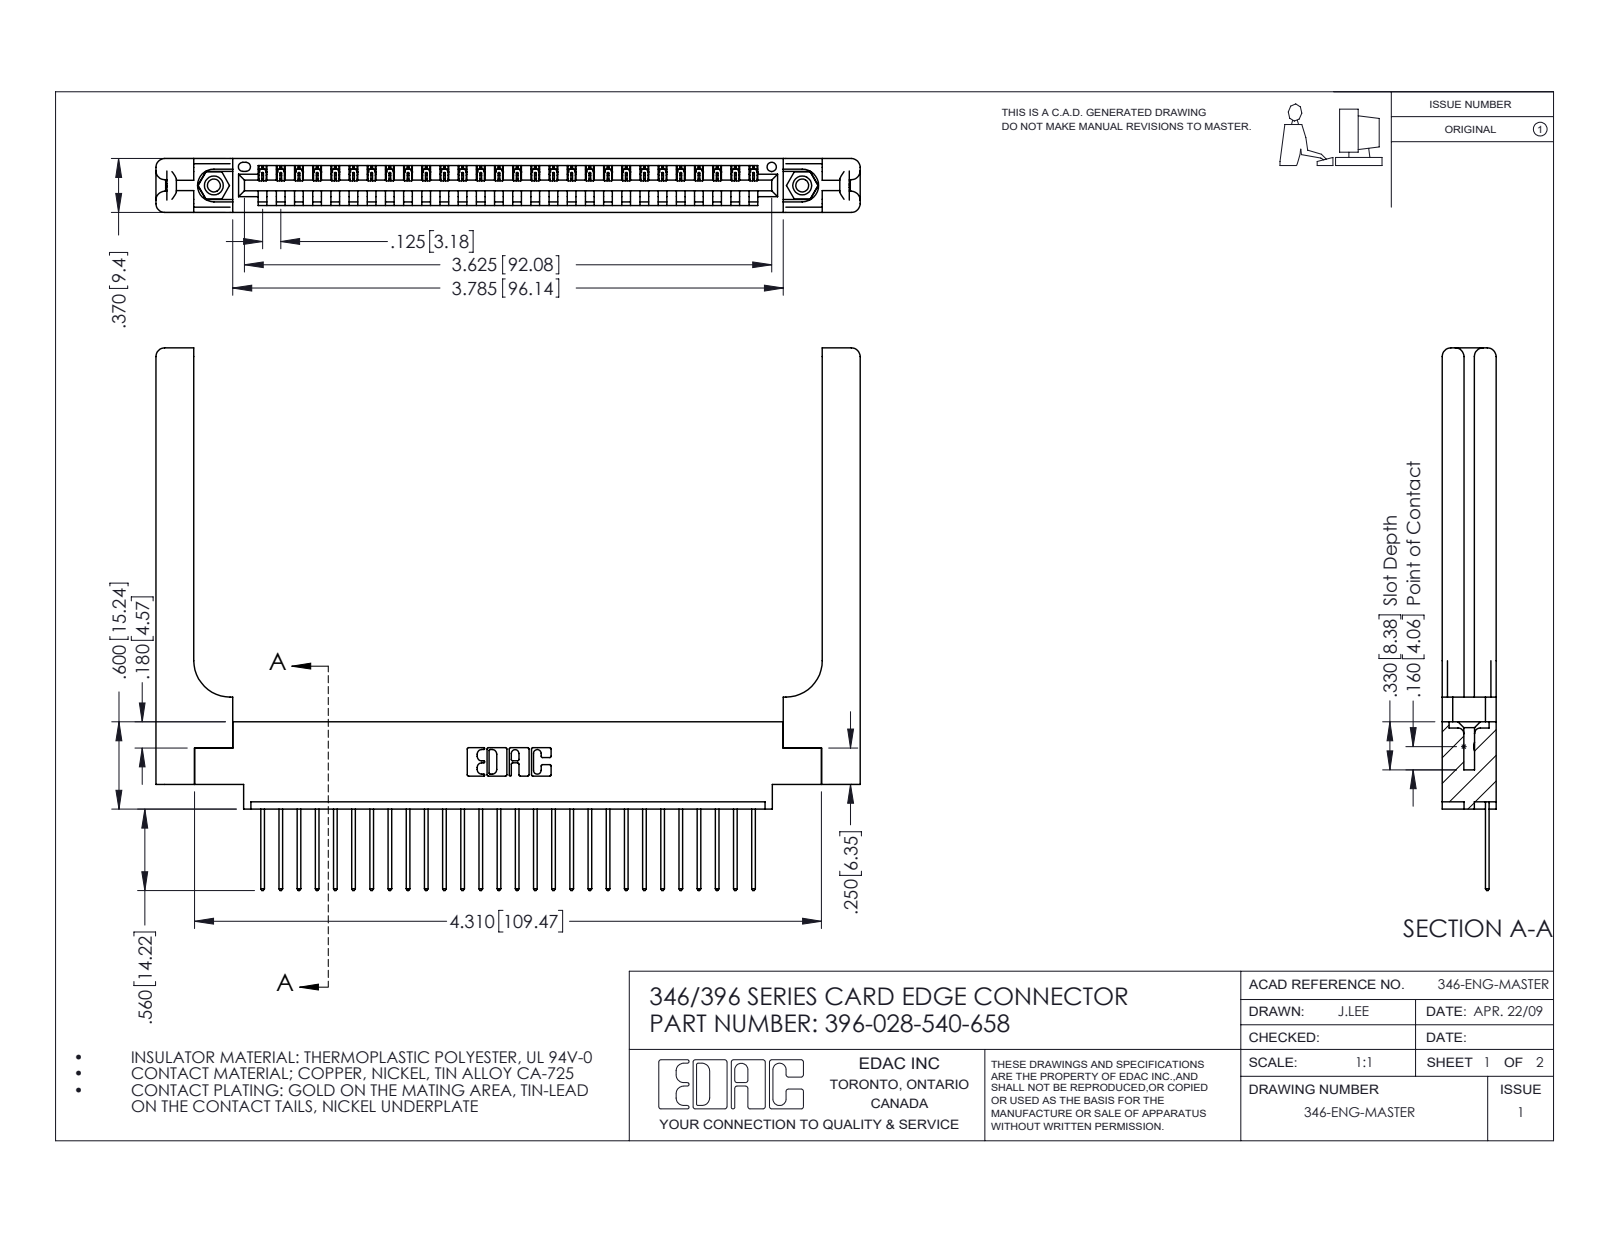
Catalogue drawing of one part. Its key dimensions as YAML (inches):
part_name: "396-028-540-658; 345-292-001_345-293-140; 345-250-001_345-250-001-102; 346 Part_0.170 Offset - 0.156 Dia-TH (+1 more)"
step_written_by: "SolidWorks 2016 (CONFIG_CONTROL_DESIGN)"
units: inches
bodies: {solids: 33, faces: 2006, planar: 1348, cylindrical: 598, other: 60}
overall_size: [4.841, 3.73, 0.37]
volume: 1.164
surface_area: 30.85
round_holes:
  - {diameter: 0.089, count: 2}
  - {diameter: 0.125, count: 2}
  - {diameter: 0.156, count: 2}
  - {diameter: 0.064, count: 1}
round_bosses_or_shafts:
  - {diameter: 0.155, count: 2}
partial_cylinders:
  - {radius: 0.006, count: 56}
  - {radius: 0.01, count: 56}
  - {radius: 0.01, count: 22}
  - {radius: 0.06, count: 16}
  - {radius: 0.007, count: 6}
  - {radius: 0.031, count: 6}
  - {radius: 0.026, count: 3}
  - {radius: 0.03, count: 2}
face_to_face_distances: [0.37, 0.072, 0.048, 0.322, 0.148, 0.15, 0.25, 0.298, 0.025, 0.076]
hole_center_spacings: [0.246, 3.837, 4.045]
